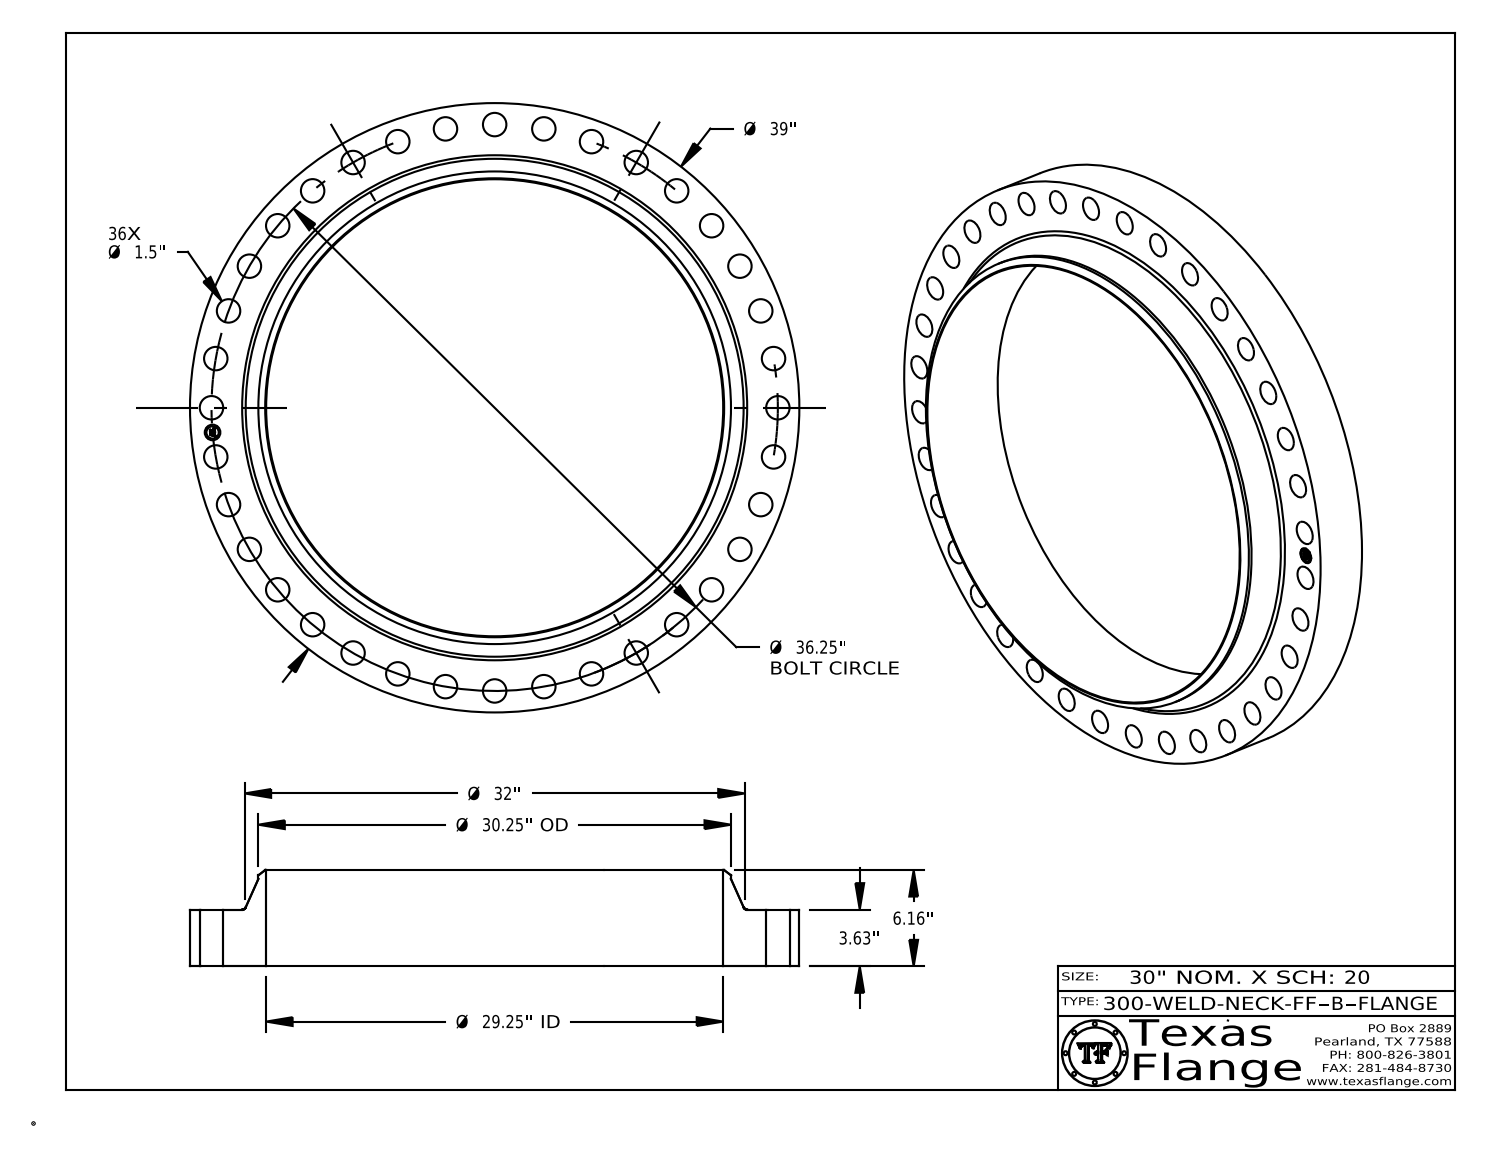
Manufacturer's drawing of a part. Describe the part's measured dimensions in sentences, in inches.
The part is named "300-WELD-NECK-FF, Series B". Its 3-D file was written by "CATIA V5 STEP AP214 (AUTOMOTIVE_DESIGN)". It is 1 solid with 472 faces: 368 planar, 98 cylindrical and 6 other. Overall it measures 39 by 39 by 6.16 inches. Its volume is 1 861 cubic inches and its surface area 2 698 square inches. Round holes: 36 of diameter 1.5, 1 of diameter 1, 1 of diameter 29.25. Round bosses or shafts: 8 of diameter 0.061, 1 of diameter 39, 1 of diameter 30.25, 1 of diameter 0.788. The main face-to-face distances are 3.63, 6.16, 2.53, 3.615, 0.015, 2.545, 0.298, 0.293, 0.019, 0.055. The hole center spacings are 18.125, 9.382, 27.769, 25.633, 35.699, 18.125, 36.112, 6.295.
